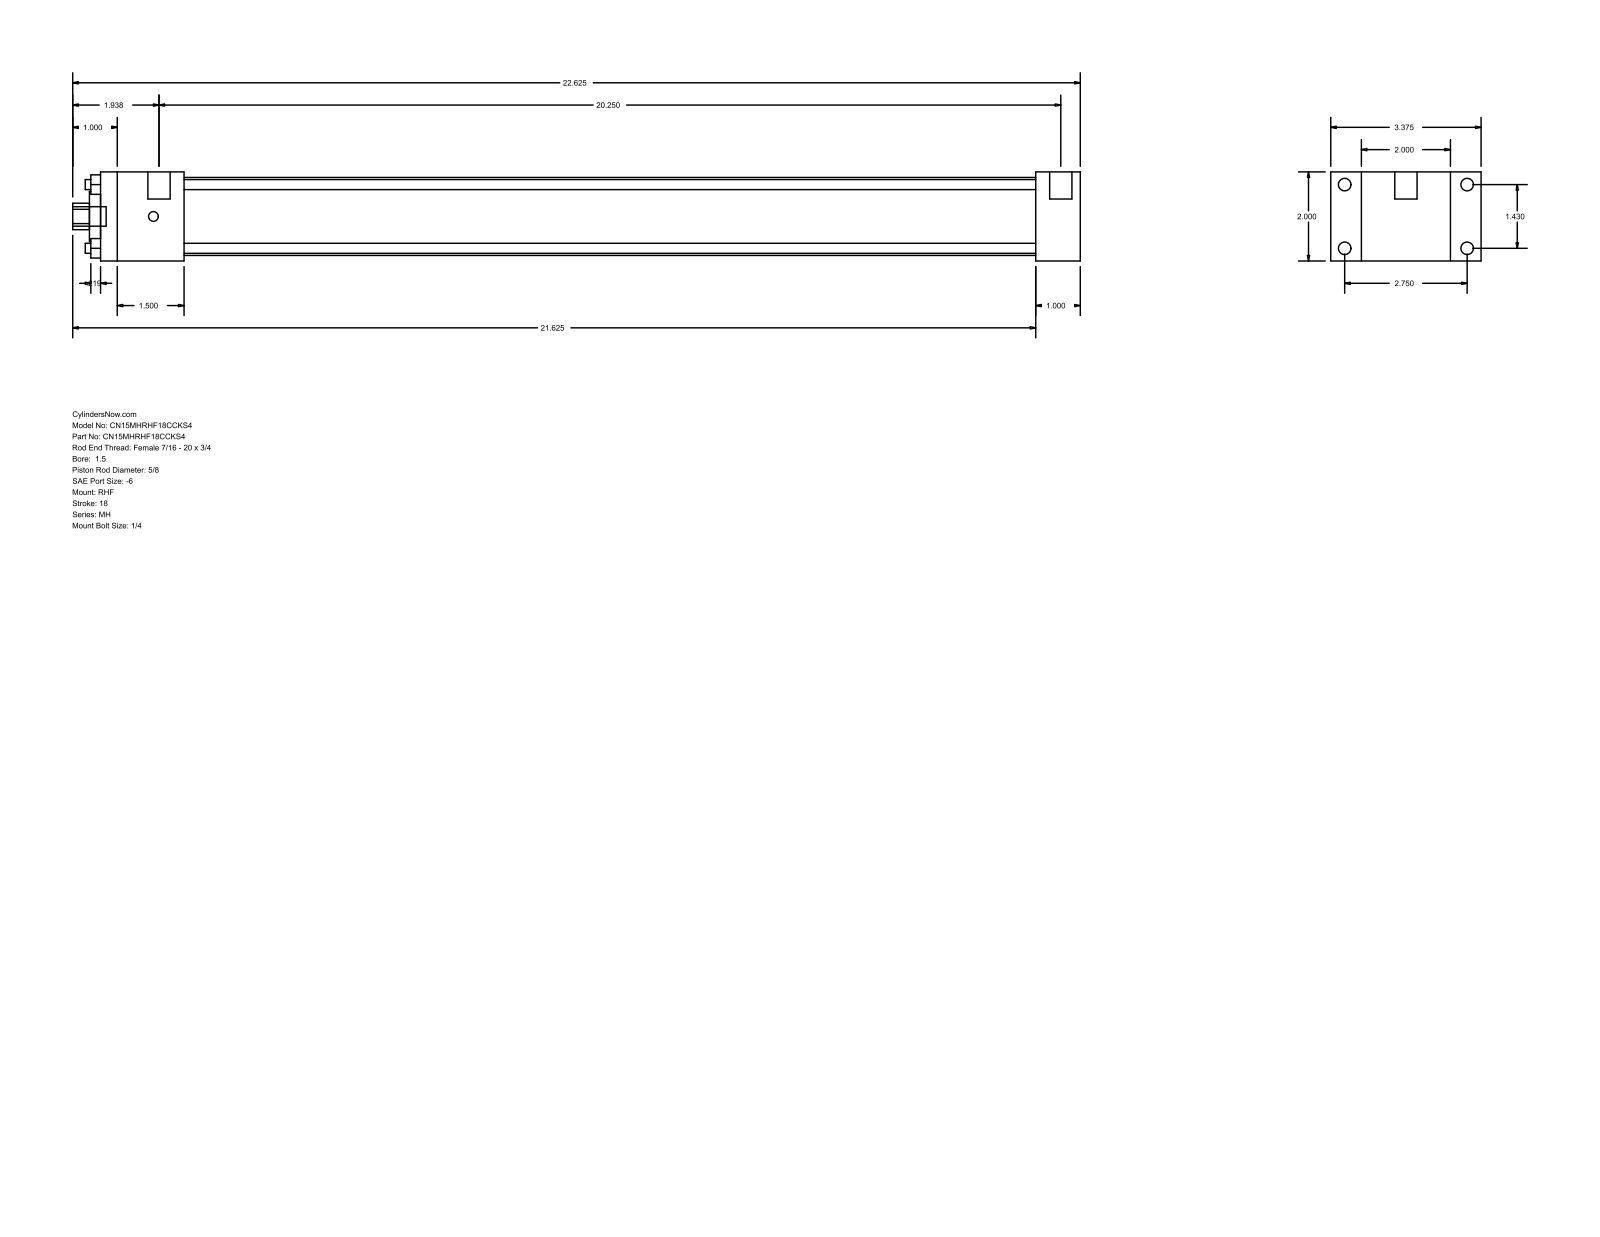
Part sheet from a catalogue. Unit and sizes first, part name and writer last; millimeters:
Units: millimetres
Overall size (bounding box): 574.67 × 85.72 × 50.8
Round holes (diameter × count): ⌀5.71 ×4, ⌀15.88 ×1, ⌀28.57 ×1, ⌀44.45 ×1
Round bosses / shafts (diameter × count): ⌀7.14 ×4, ⌀5.56 ×4, ⌀12.7 ×2, ⌀11.11 ×1
Partial cylindrical surfaces — rounded edges, fillets, slot ends (radius × count): R7.54 ×1
Main face-to-face distances: 50.8, 17.46, 68.26, 25.4, 533.39, 558.79, 85.72, 47.62, 485.77, 511.17
Hole centre spacings: 25.68, 36.32, 51.36
Bodies: 0 solids, 88 faces (60 planar, 28 cylindrical, 0 other)
Part name (STEP PRODUCT): MH_RHF__0150_0.625
STEP written by: GSSL Pune (CONFIG_CONTROL_DESIGN)
